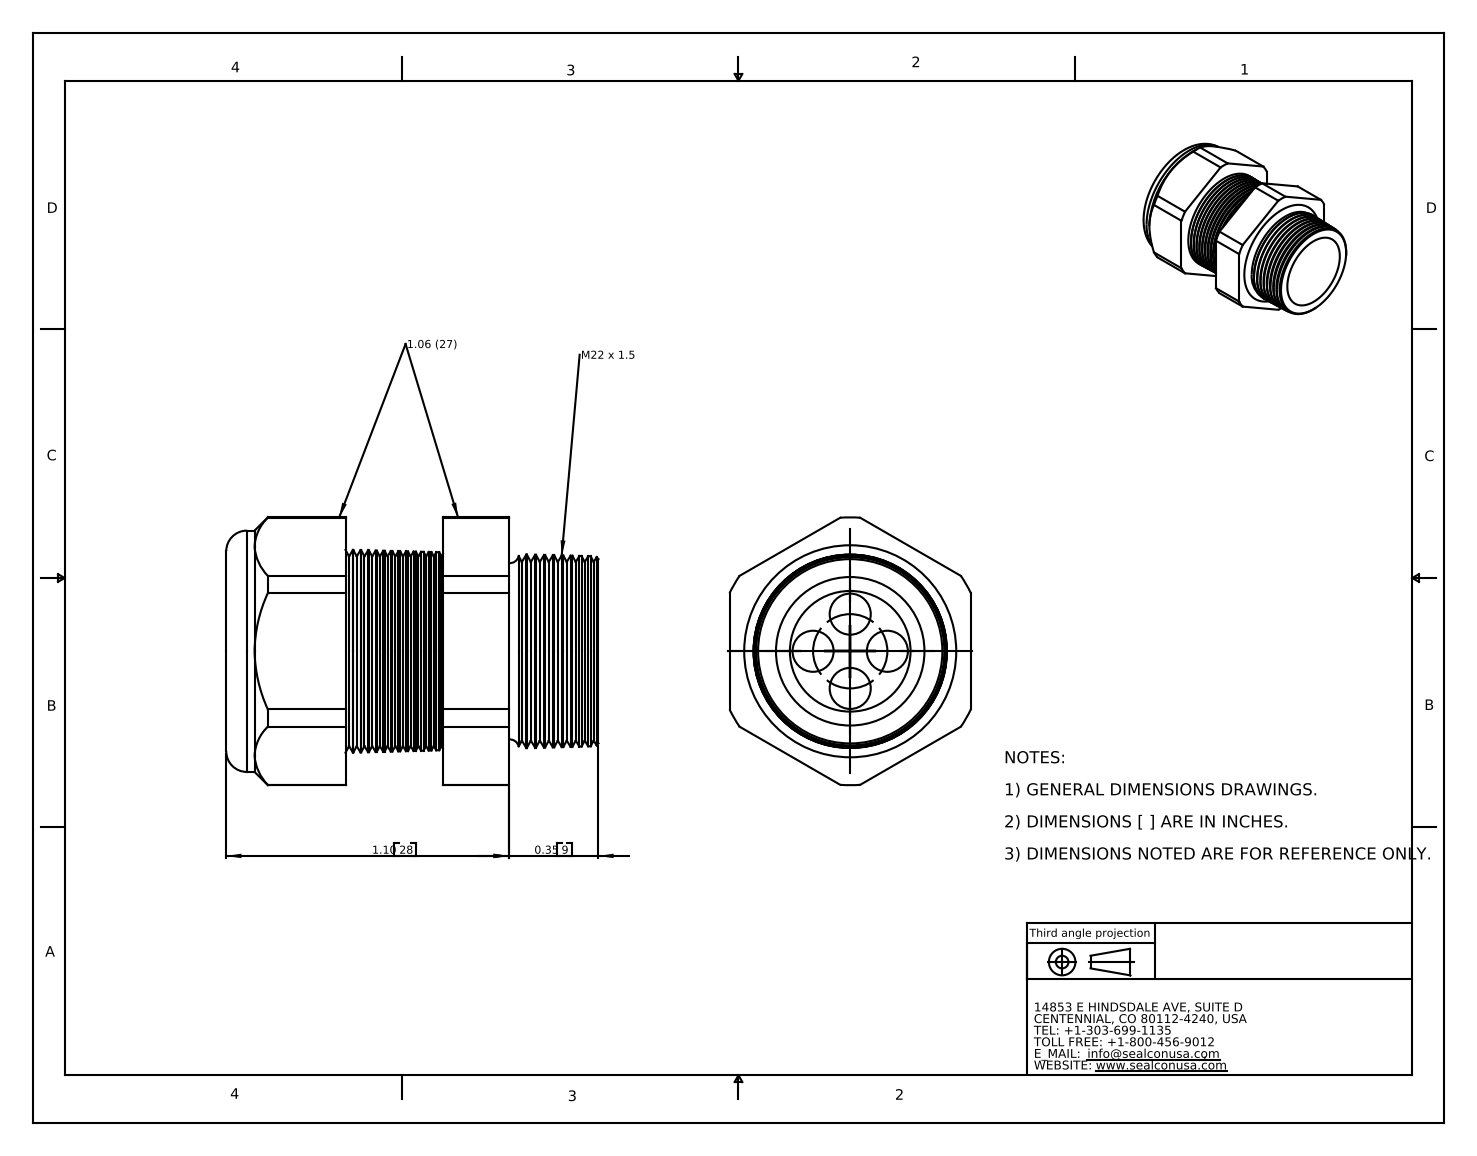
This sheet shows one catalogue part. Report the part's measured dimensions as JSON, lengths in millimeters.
{"part_name": "CD22M3-GY", "step_written_by": "SolidWorks 2007 (CONFIG_CONTROL_DESIGN)", "units": "millimeters", "bodies": {"solids": 2, "faces": 194, "planar": 20, "cylindrical": 28, "other": 146}, "overall_size": [36.8, 26.5, 23.9], "volume_mm3": 9440, "surface_area_mm2": 6658, "round_holes": [[4.1, 4], [11.4, 1], [11.9, 1]], "round_bosses_or_shafts": [[23.9, 1]], "partial_cylinders_radius": [[13.3, 1]], "face_to_face_distances": [23.9, 21.4, 11.8, 9.7, 27.9, 16.1, 6.5, 36.8, 25, 15.4], "hole_center_spacings": [3.7, 5.2, 7.3]}
